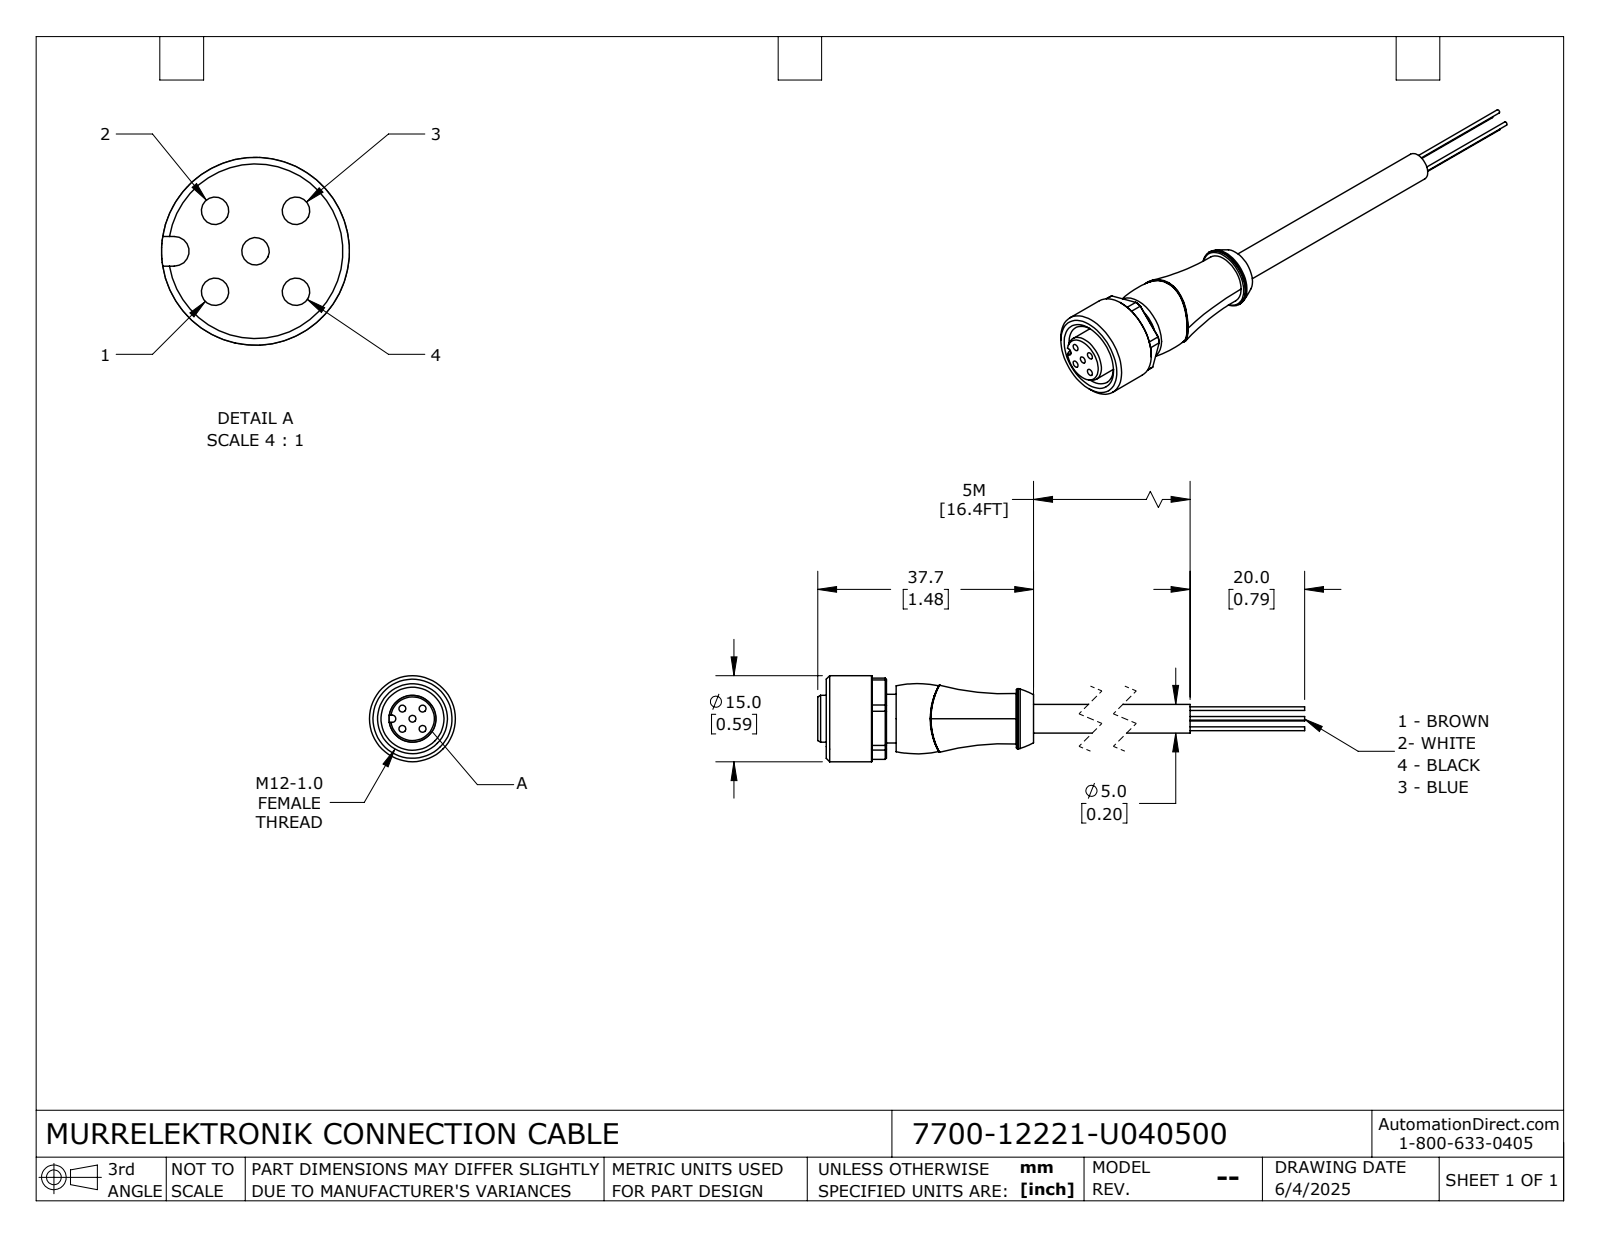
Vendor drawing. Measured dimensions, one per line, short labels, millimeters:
name: 7700-12221-U040500
written by: SolidWorks 2024 (CONFIG_CONTROL_DESIGN)
unit: mm
bodies: 1 solid, 110 faces (36 planar, 39 cylindrical, 35 other)
size: 102.7 × 15 × 15
volume: 4 577 mm³; area: 3 233 mm²
holes: 5× ⌀1.2, 1× ⌀11
bosses: 4× ⌀0.64, 1× ⌀15, 1× ⌀10.5, 1× ⌀8.5, 1× ⌀8.2, 1× ⌀5
rounds: 1× R0.65, 1× R7.2
face distances: 3, 25.7, 1.7, 13, 4.7, 9, 12, 13.7, 37.7, 28.7
hole spacings: 2.5, 3.53, 3.54, 5
